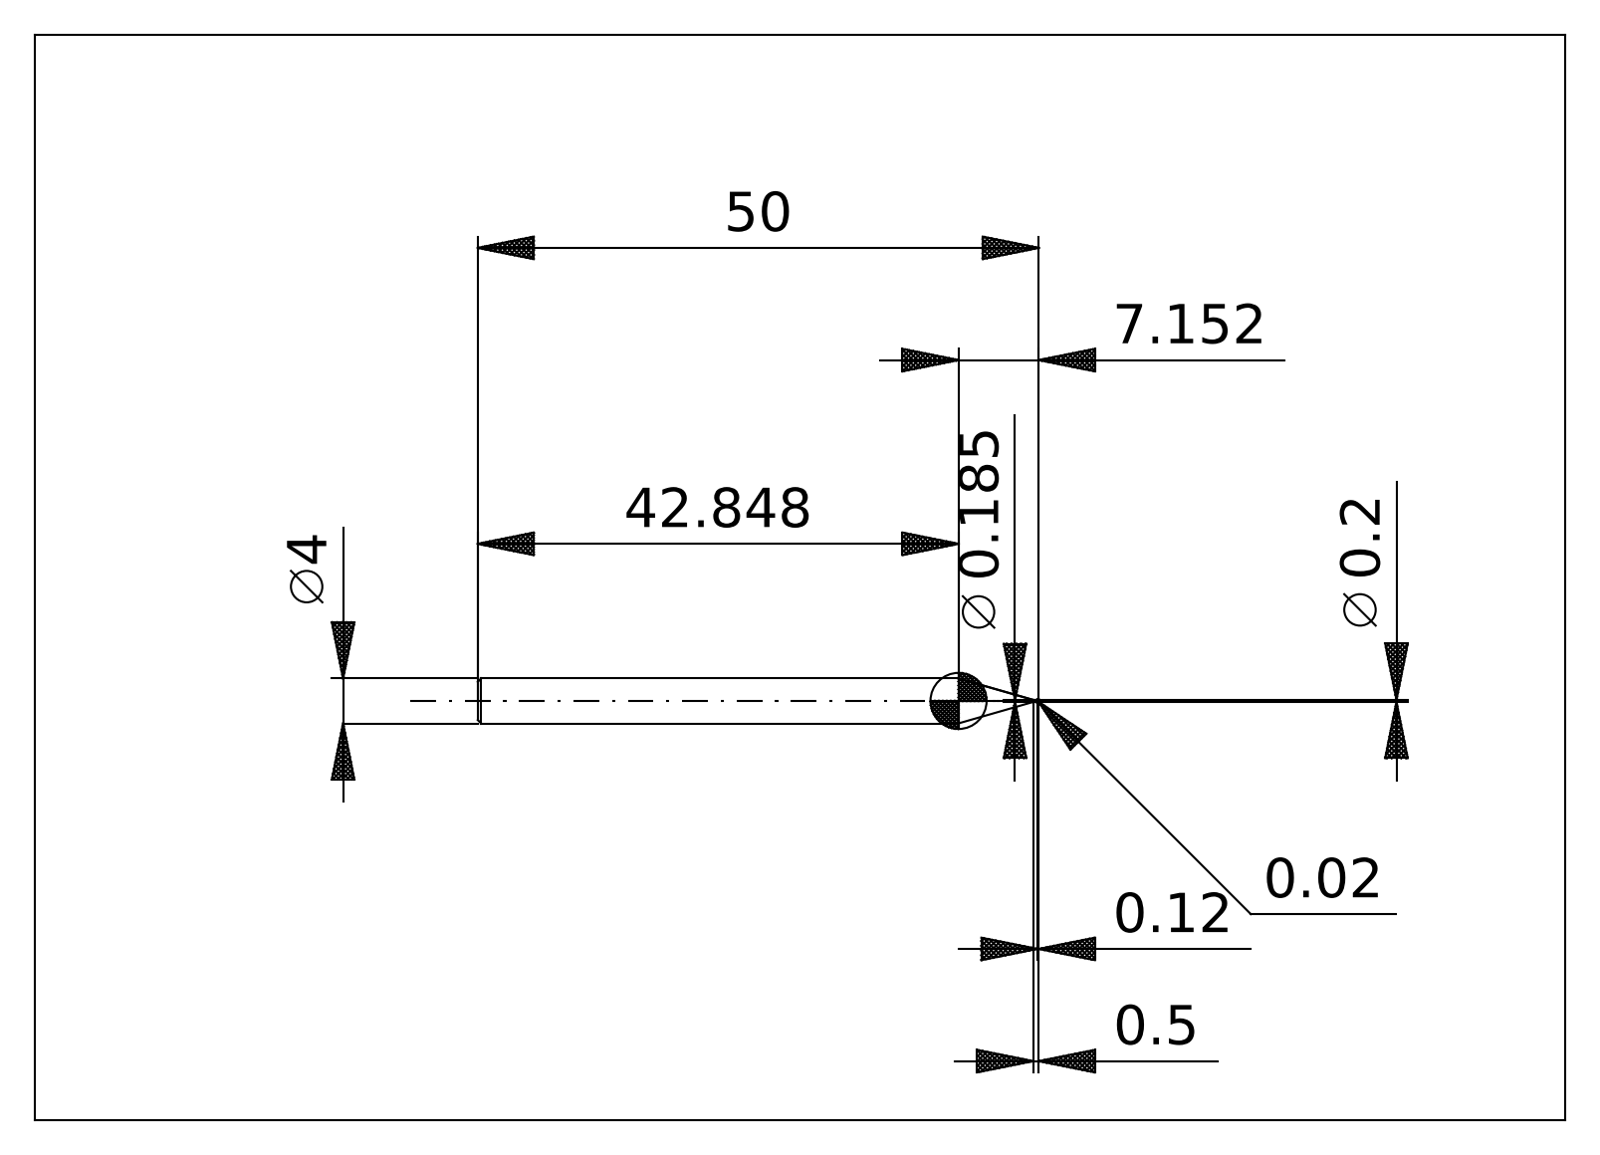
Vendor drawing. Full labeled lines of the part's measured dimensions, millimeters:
STEP written by: ACIS (automotive_design)
Units: millimetres
Bodies: 2 solids, 26 faces (6 planar, 8 cylindrical, 12 other)
Overall size (bounding box): 50 × 4 × 4
Volume: 567 mm³ · Surface area: 595 mm²
Round bosses / shafts (diameter × count): ⌀4 ×1
Main face-to-face distances: 50, 49.97, 49.88, 7.15, 7.12, 7.03, 42.85
